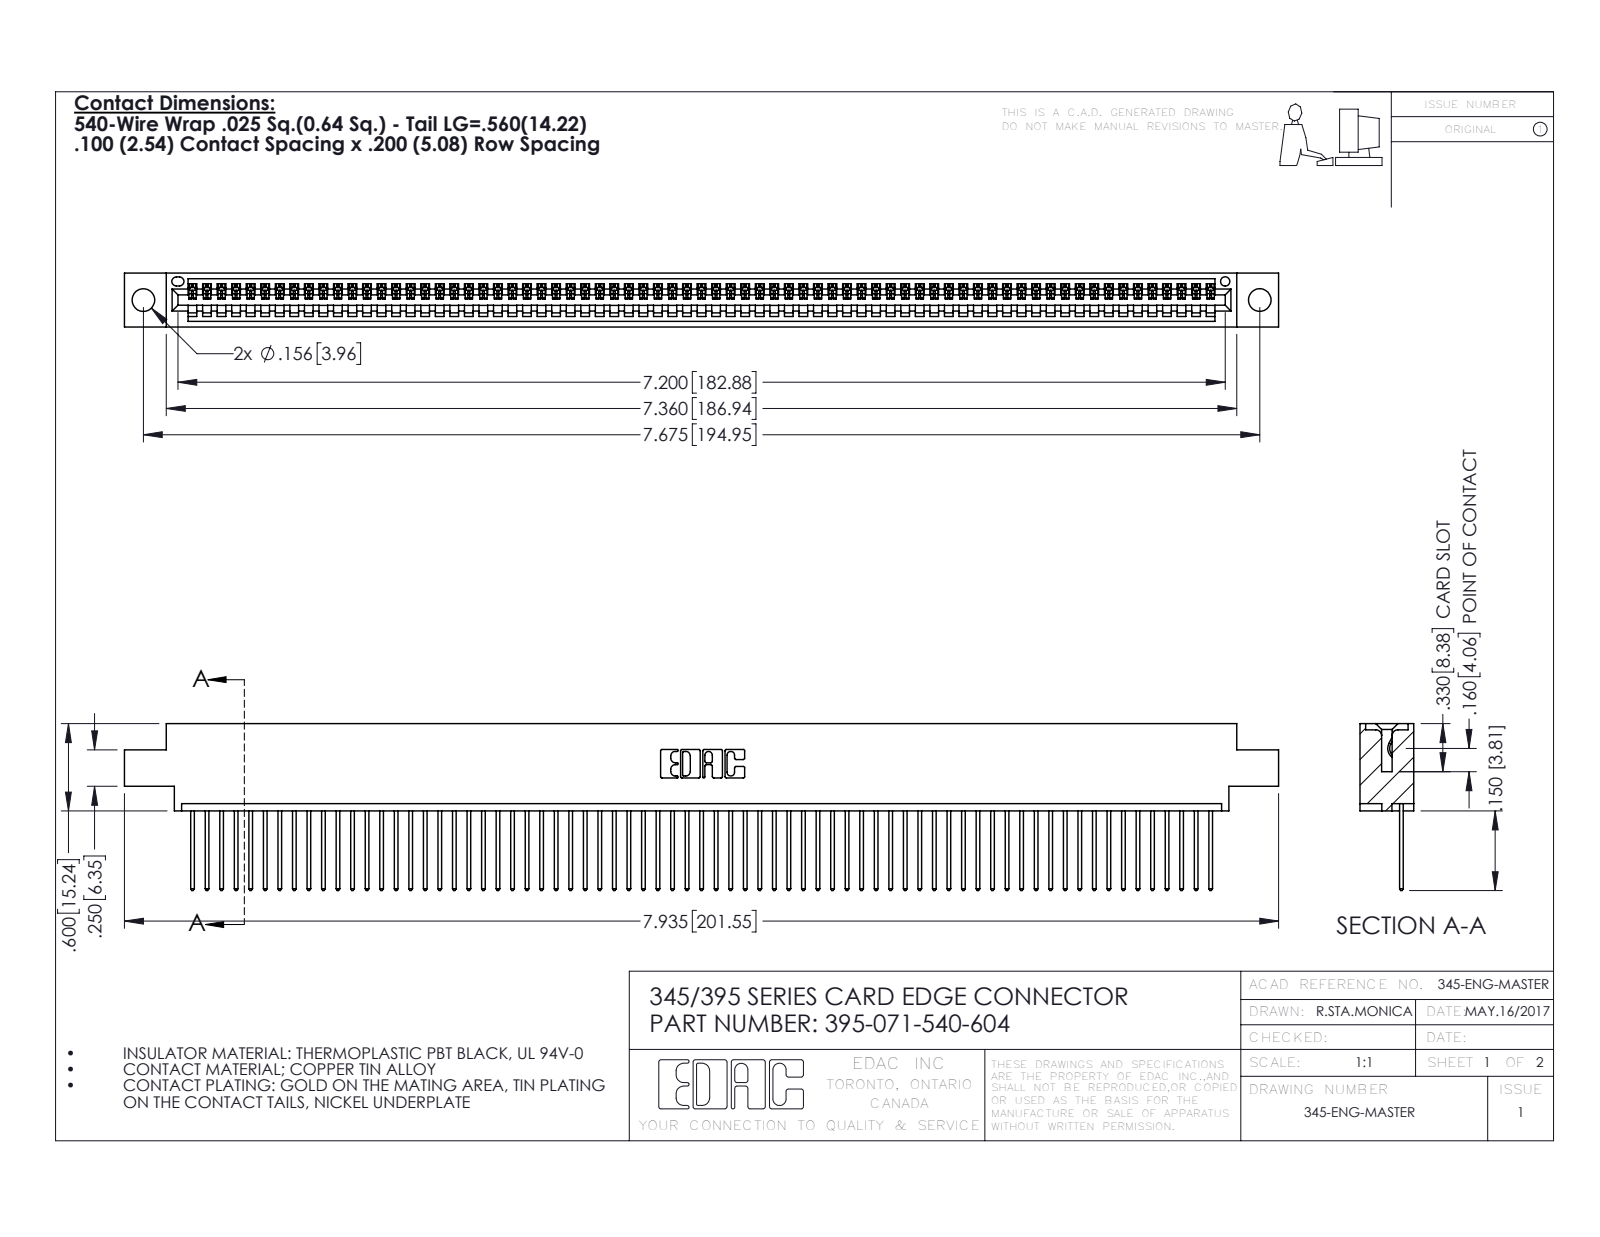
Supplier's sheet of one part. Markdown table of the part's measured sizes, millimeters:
| quantity | value |
| --- | --- |
| part name | 345-292-001_345-293-140; 395-071-540-604; 345 Part_0.170 Offset - 0.156 Dia-TH |
| STEP written by | SolidWorks 2016 (CONFIG_CONTROL_DESIGN) |
| units | millimeters |
| bodies | 72 solids, 4248 faces (2924 planar, 1324 cylindrical, 0 other) |
| overall size | 201.5 × 29.1 × 9.4 |
| volume | 19 270 mm³ |
| surface area | 26 640 mm² |
| round holes (diameter × count) | 4 × 2, 1.6 × 1 |
| partial cylindrical surfaces (radius × count) | 0.2 × 142, 0.3 × 142, 0.3 × 22, 0.2 × 6, 0.8 × 6, 0.7 × 3, 0.8 × 2, 1 × 2 |
| main face-to-face distances | 1.8, 7.6, 9.4, 2.5, 6.9, 0.6, 5.1, 5.7, 4.4, 3.8 |
| hole center spacings | 6.9, 189, 194.9 |
